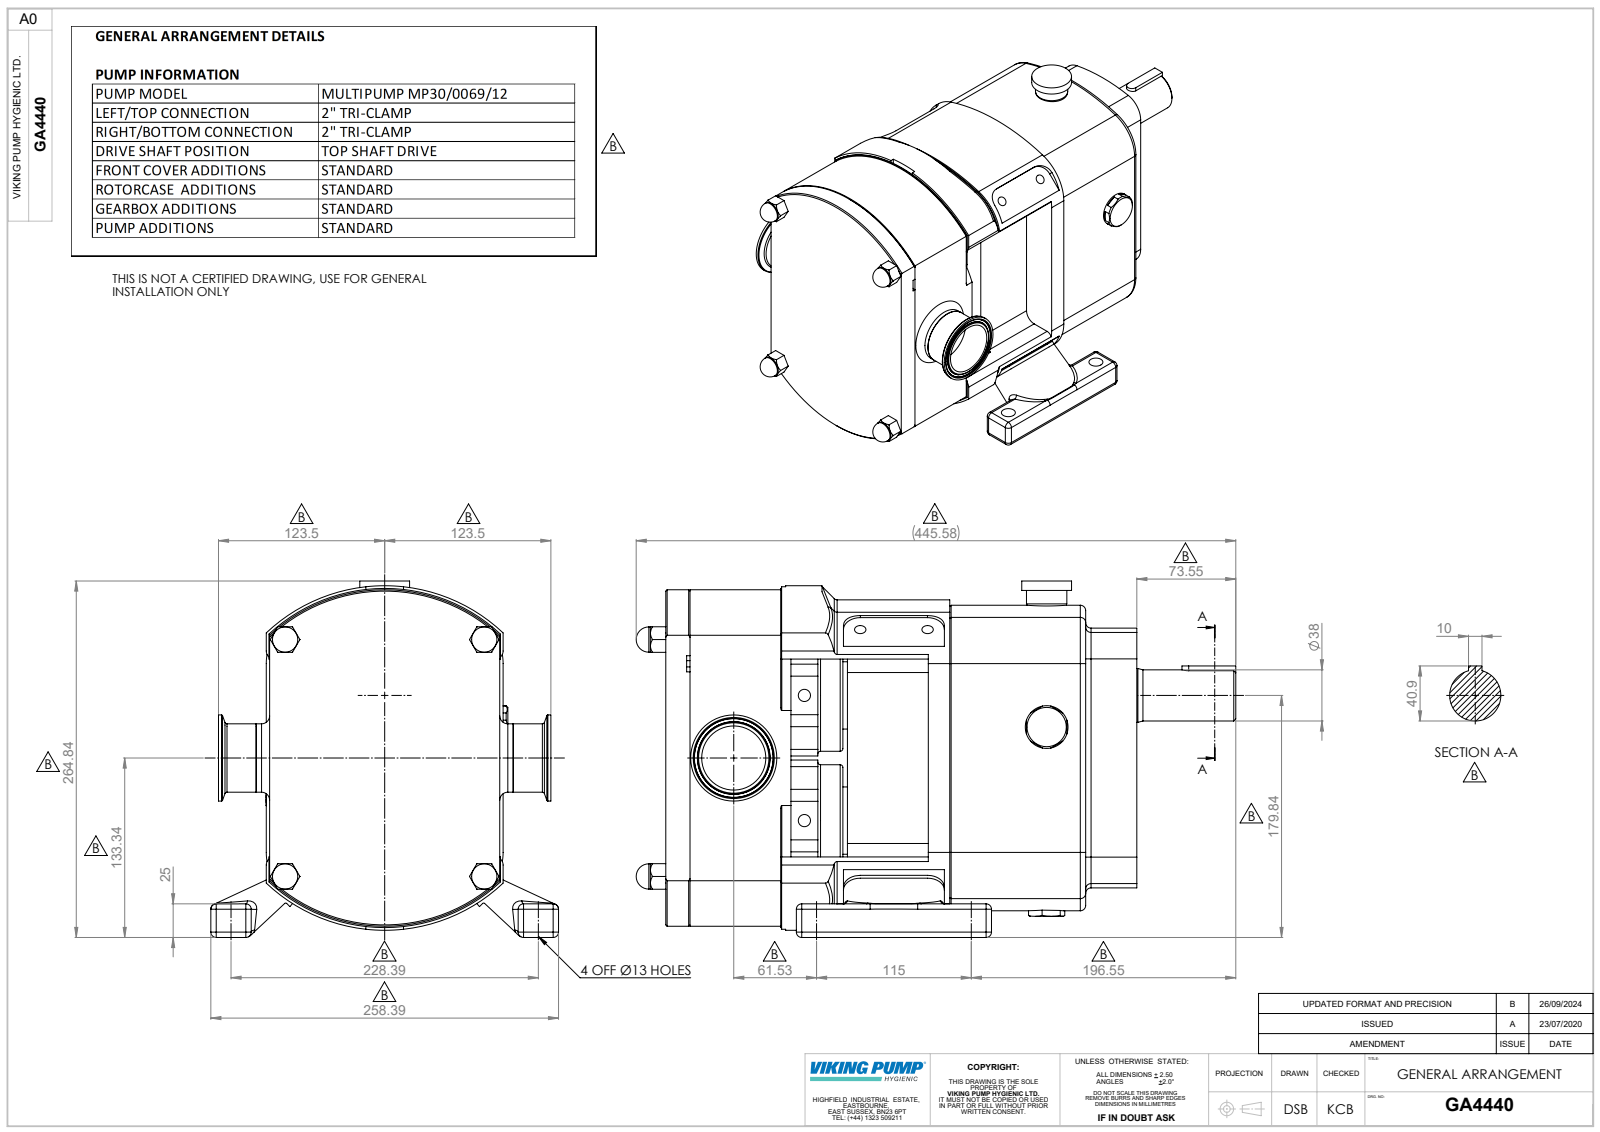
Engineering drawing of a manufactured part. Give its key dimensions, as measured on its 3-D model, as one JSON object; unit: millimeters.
{"part_name": "Copy of Z94-5121-33 - 2 INCH^GA4440; GA4440; Copy of CP30-0069-12 H T^GA4440", "step_written_by": "SolidWorks 2023 (AUTOMOTIVE_DESIGN)", "units": "millimeters", "bodies": {"solids": 3, "faces": 736, "planar": 267, "cylindrical": 238, "other": 231}, "overall_size": [445.58, 264.84, 258.38], "volume_mm3": 11460000, "surface_area_mm2": 524443, "round_holes": [[8.5, 4], [10.11, 4], [13, 4], [9.09, 2], [35, 1], [47.65, 1]], "round_bosses_or_shafts": [[18.8, 4], [83, 2], [50, 2], [64, 1], [50.8, 1], [40.01, 1], [38, 1], [37, 1]], "partial_cylinders_radius": [[4, 44], [1, 16], [10, 12], [6, 10], [12.5, 4], [12.57, 4], [12.6, 4], [20, 4]], "face_to_face_distances": [1.5, 169.5, 139, 38, 134.98, 29, 215.05, 350.03, 30.5, 140.5], "hole_center_spacings": [63.64, 50.05, 70.13, 90, 115, 127.18, 205.62, 228.38]}
